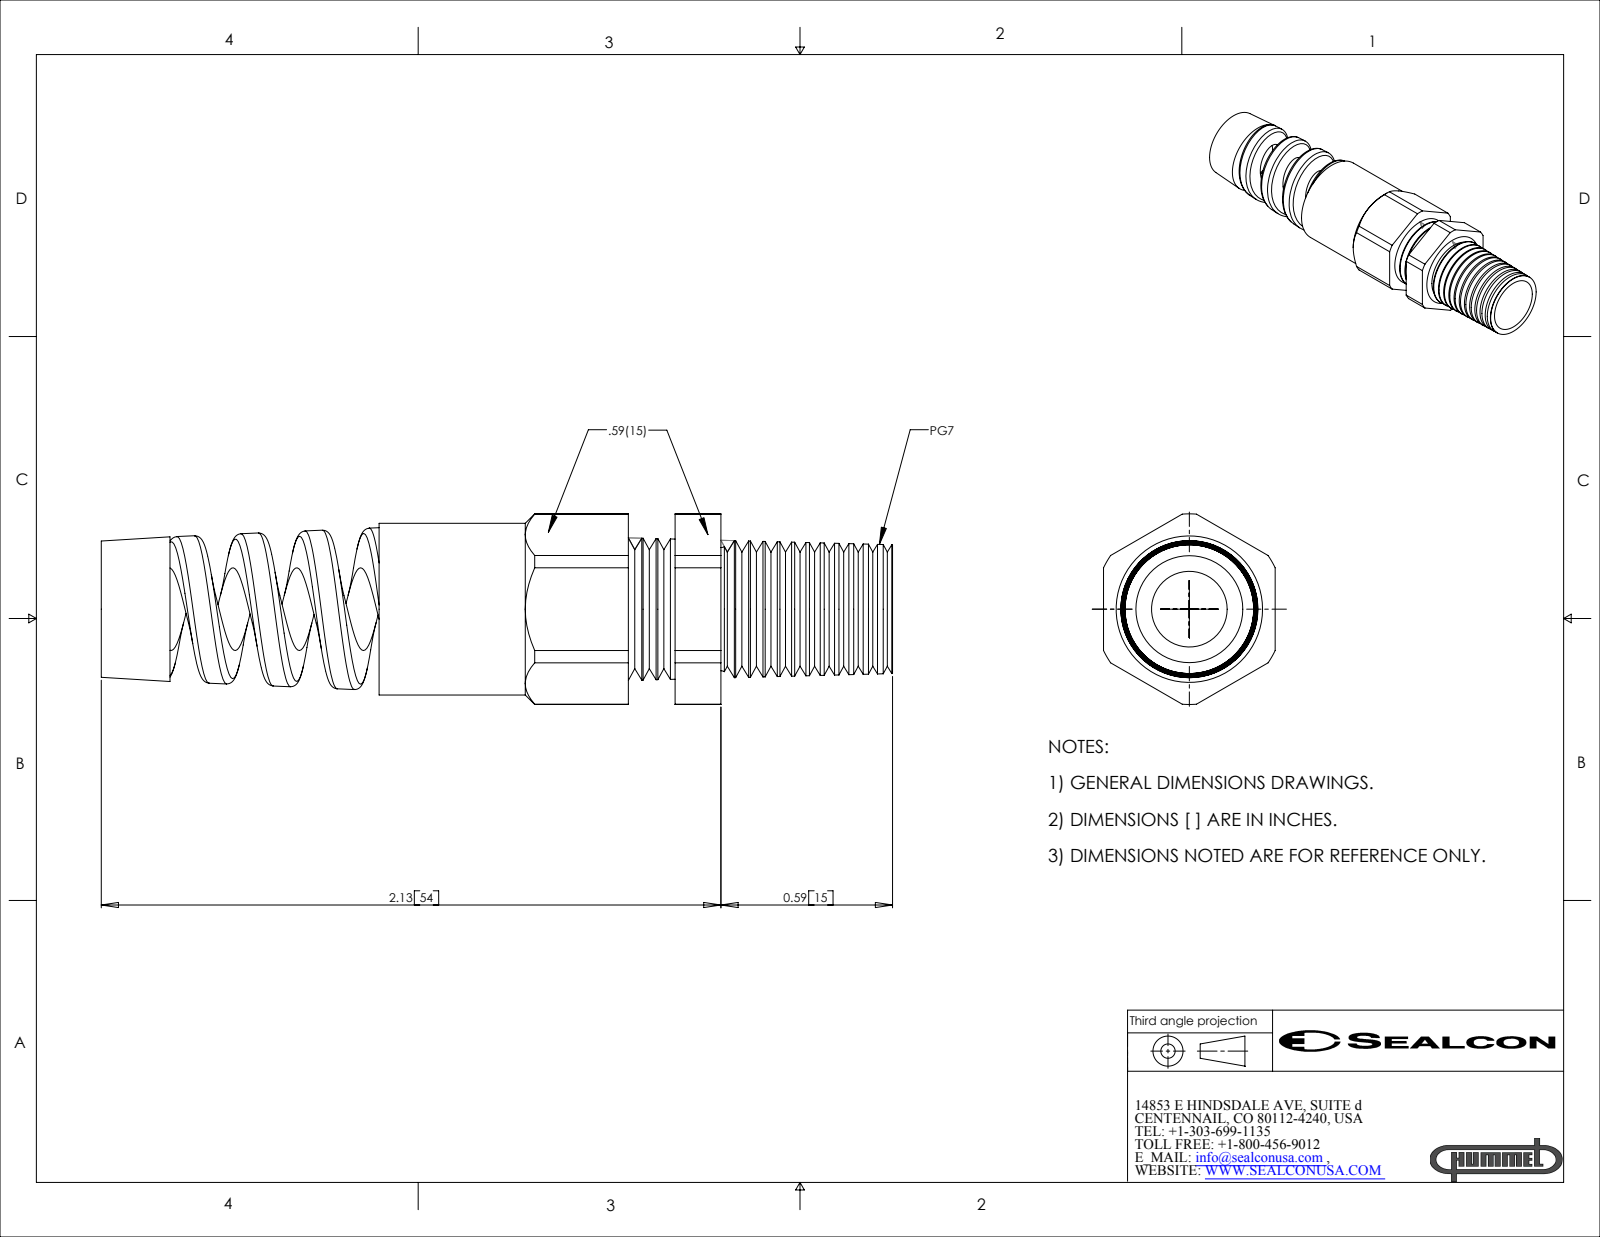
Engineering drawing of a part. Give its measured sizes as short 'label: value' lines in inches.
name: CF07CA-GY
written by: SolidWorks 2007 (CONFIG_CONTROL_DESIGN)
unit: in
bodies: 2 solids, 177 faces (24 planar, 33 cylindrical, 120 other)
size: 2.72 × 0.655 × 0.59
volume: 0.365 in³; area: 8.986 in²
holes: 1× ⌀0.26, 1× ⌀0.284, 1× ⌀0.313
bosses: 1× ⌀0.59, 1× ⌀0.367
rounds: 1× R0.327
face distances: 0.59, 1.018, 0.157, 0.857, 0.161, 1.175, 0.319, 0.955, 1.812, 1.973
